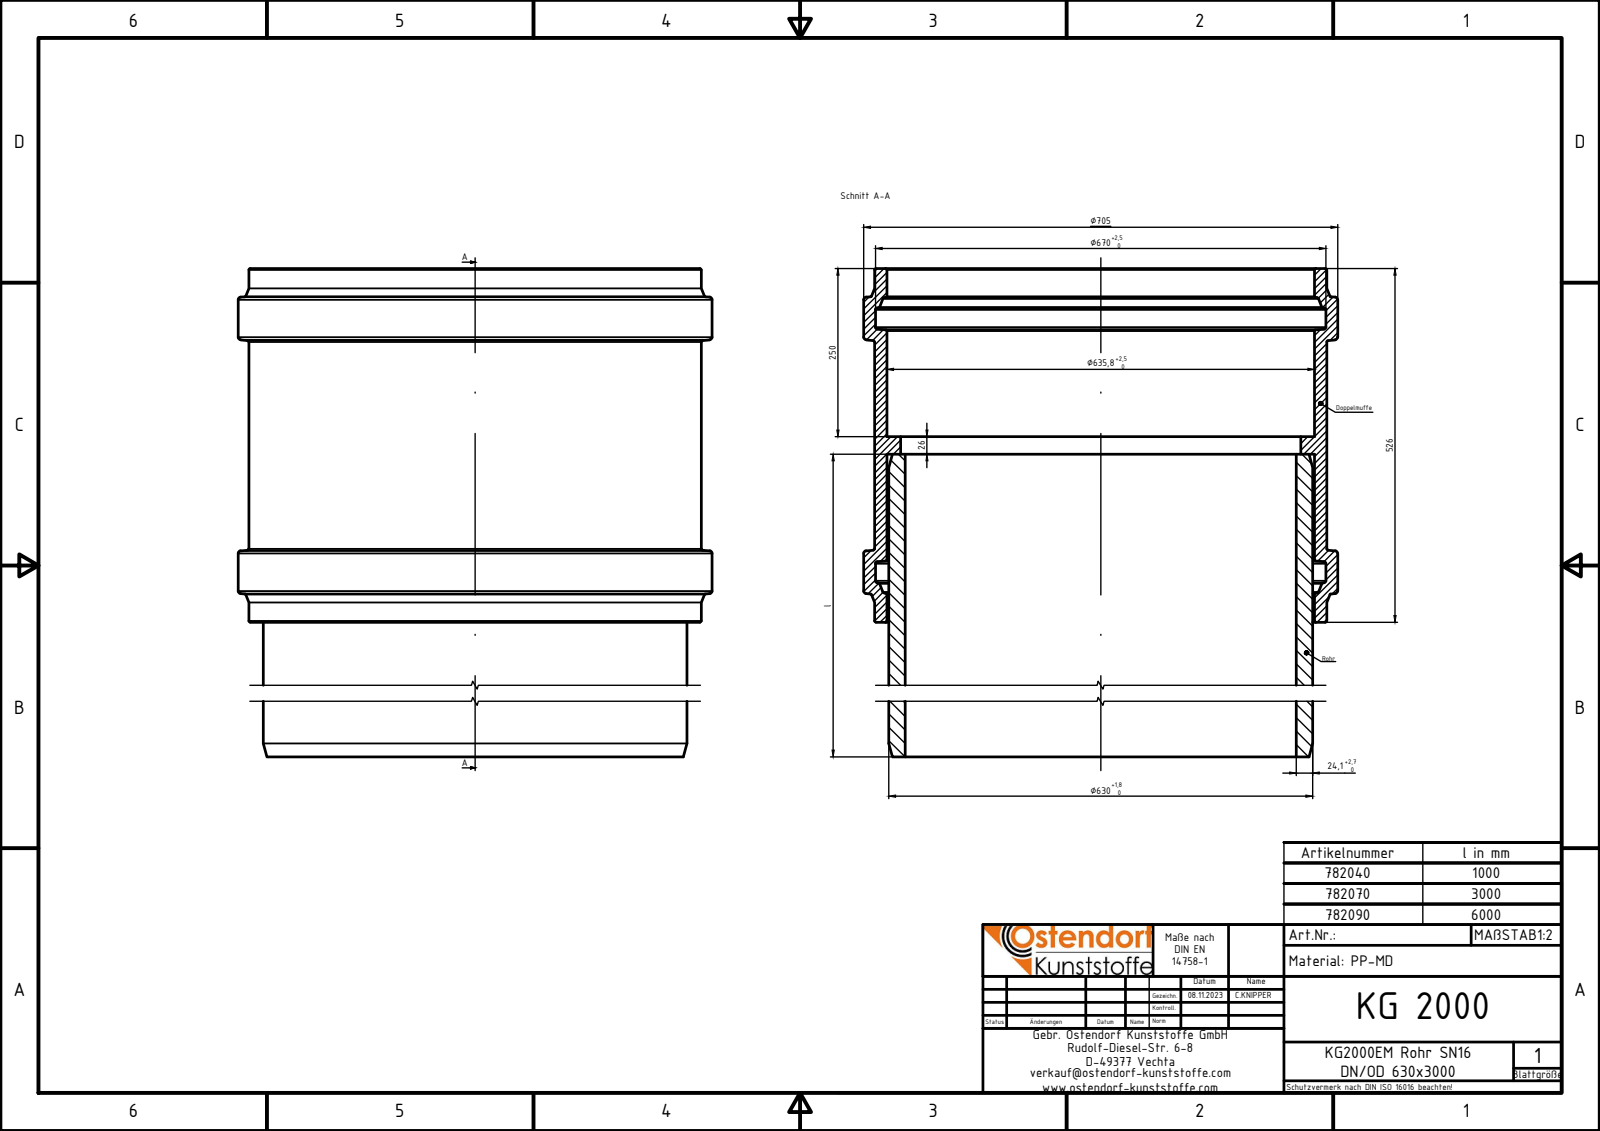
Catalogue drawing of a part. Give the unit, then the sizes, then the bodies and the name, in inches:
Units: inches
Overall size (bounding box): 128.976 × 27.748 × 27.748
Round holes (diameter × count): ⌀22.906 ×1, ⌀23.417 ×1, ⌀25.031 ×1, ⌀26.378 ×1
Round bosses / shafts (diameter × count): ⌀27.748 ×1, ⌀26.48 ×1, ⌀24.803 ×1
Main face-to-face distances: 10.866, 9.843, 119.134, 108.268, 128.976, 20.709, 118.11, 1.024
Volume: 9 776 in³ · Surface area: 21 650 in²
Bodies: 1 solid, 60 faces (6 planar, 14 cylindrical, 40 other)
Part name (STEP PRODUCT): 782070z
STEP written by: Autodesk Inventor 2024 (AUTOMOTIVE_DESIGN)
